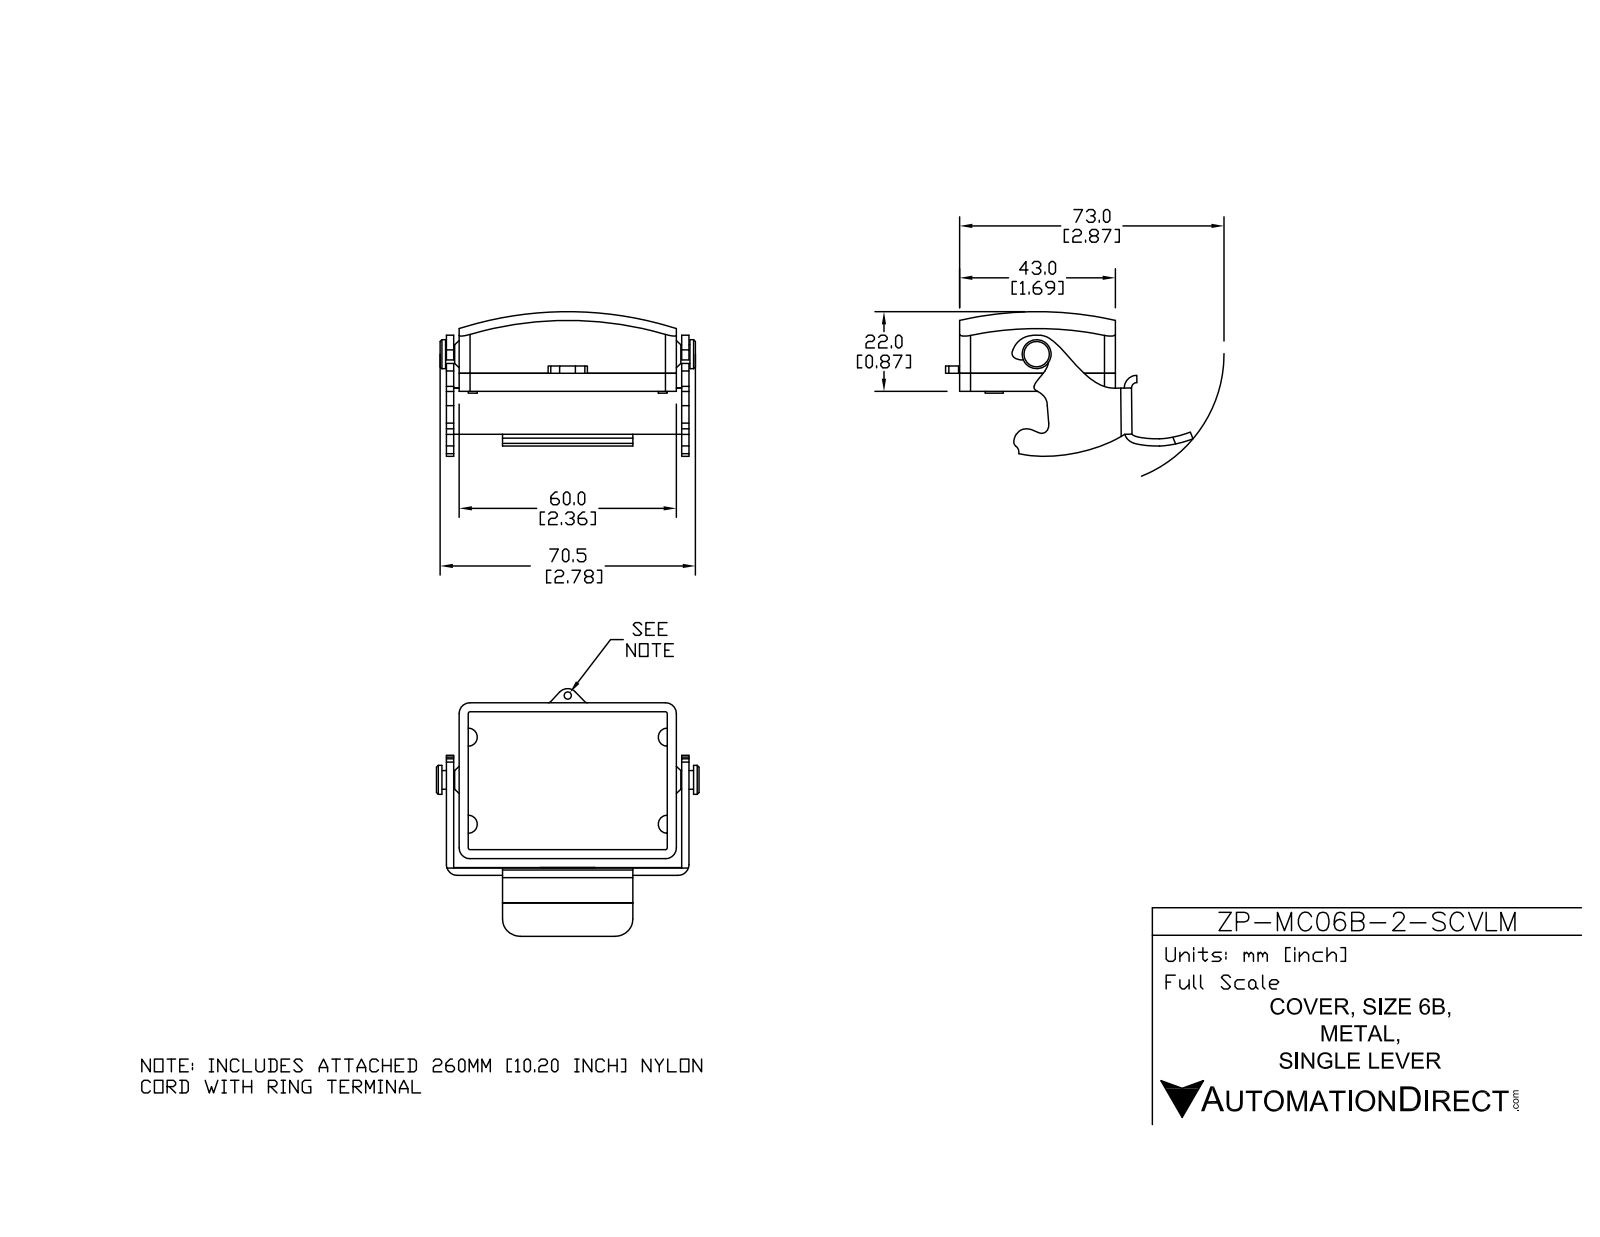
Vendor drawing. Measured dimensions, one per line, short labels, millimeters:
name: ZP-MC06B-2-SCVLM
written by: SolidWorks 2011 (AUTOMOTIVE_DESIGN)
unit: mm
bodies: 5 solids, 204 faces (75 planar, 98 cylindrical, 31 other)
size: 77.46 × 72.5 × 36.08
volume: 18 490 mm³; area: 20 089 mm²
holes: 1× ⌀2
bosses: 2× ⌀8, 2× ⌀5.17
rounds: 13× R0.5, 6× R0.12, 6× R3, 5× R2, 4× R1, 4× R2.5, 3× R4, 2× R0.75
face distances: 2.5, 1.15, 41, 1.25, 61.25, 2.4, 62.4, 63.65, 4.9, 59.9
